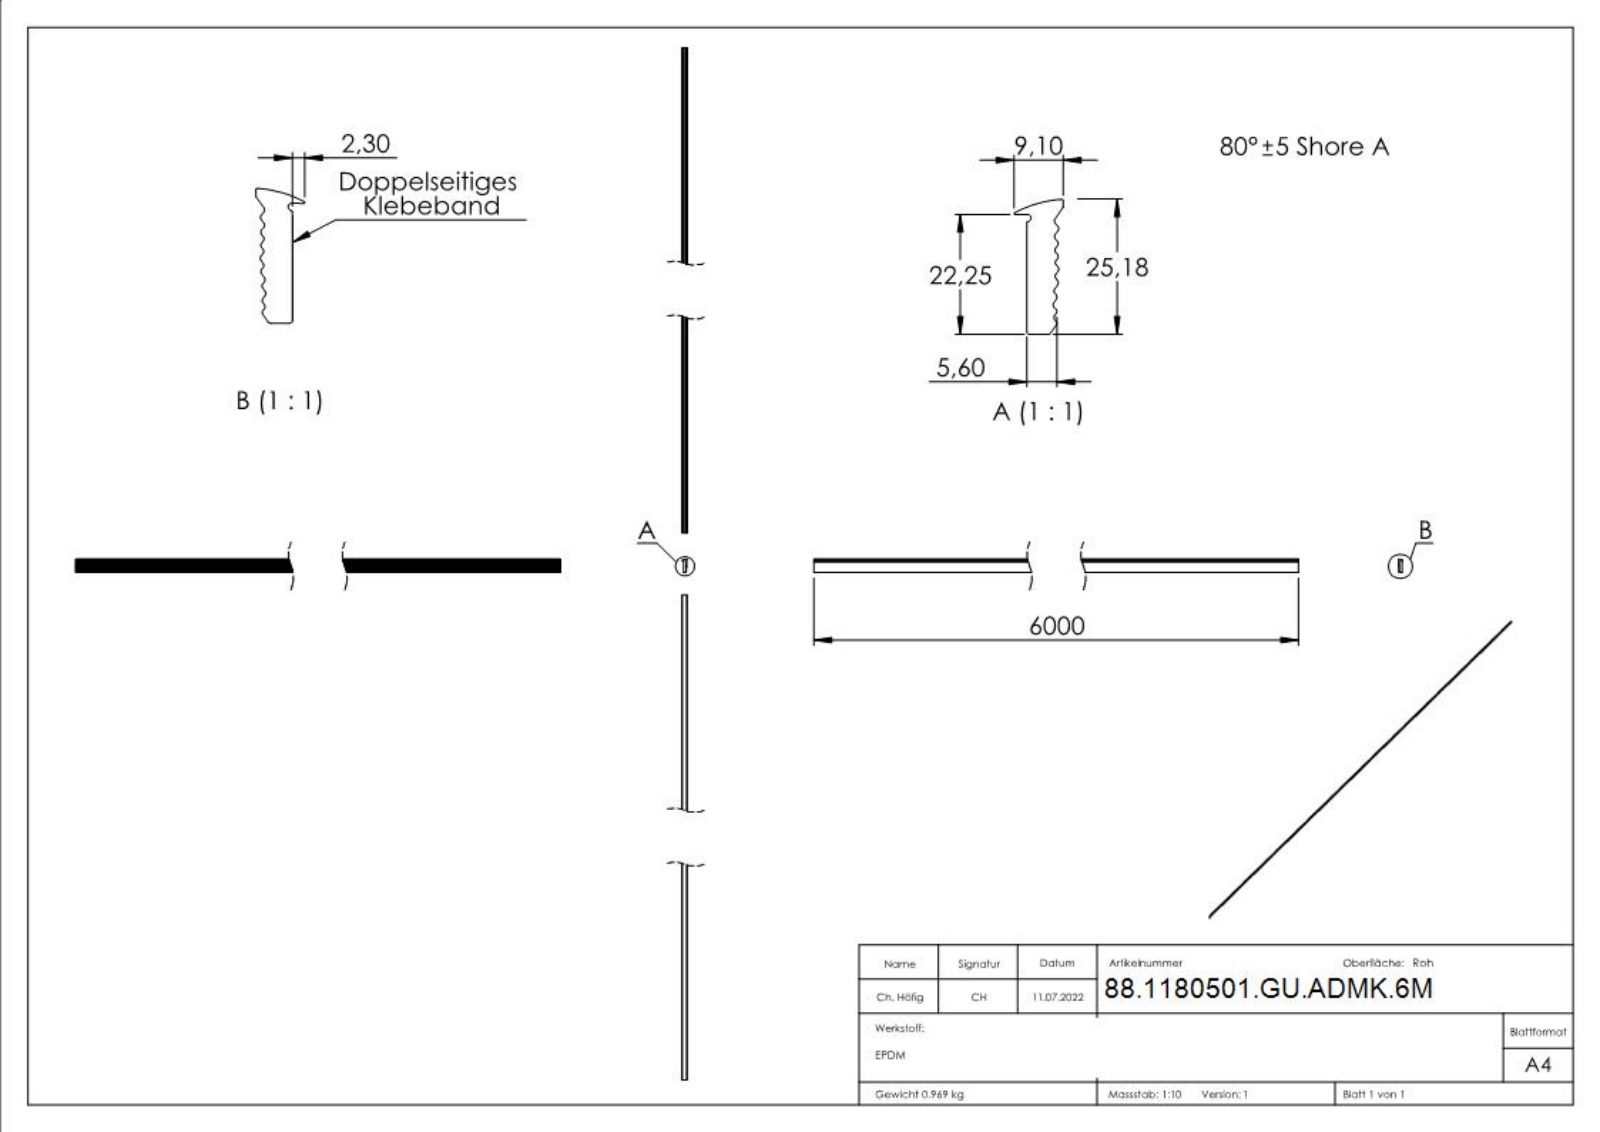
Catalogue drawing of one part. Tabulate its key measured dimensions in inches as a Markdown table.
| quantity | value |
| --- | --- |
| part name | 80501-GU-ADMK-6M |
| STEP written by | SolidWorks 2018 (CONFIG_CONTROL_DESIGN) |
| units | inches |
| bodies | 1 solid, 392 faces (225 planar, 24 cylindrical, 143 other) |
| overall size | 236.22 × 0.988 × 0.358 |
| volume | 50.06 in³ |
| surface area | 632.8 in² |
| partial cylindrical surfaces (radius × count) | 0.024 × 10, 0.024 × 8, 0.008 × 2, 0.012 × 2, 0.028 × 1, 0.921 × 1 |
| main face-to-face distances | 0.066, 0.268, 0.053, 0.054, 0.107, 0.126, 0.06, 0.072, 0.326, 0.398 |
